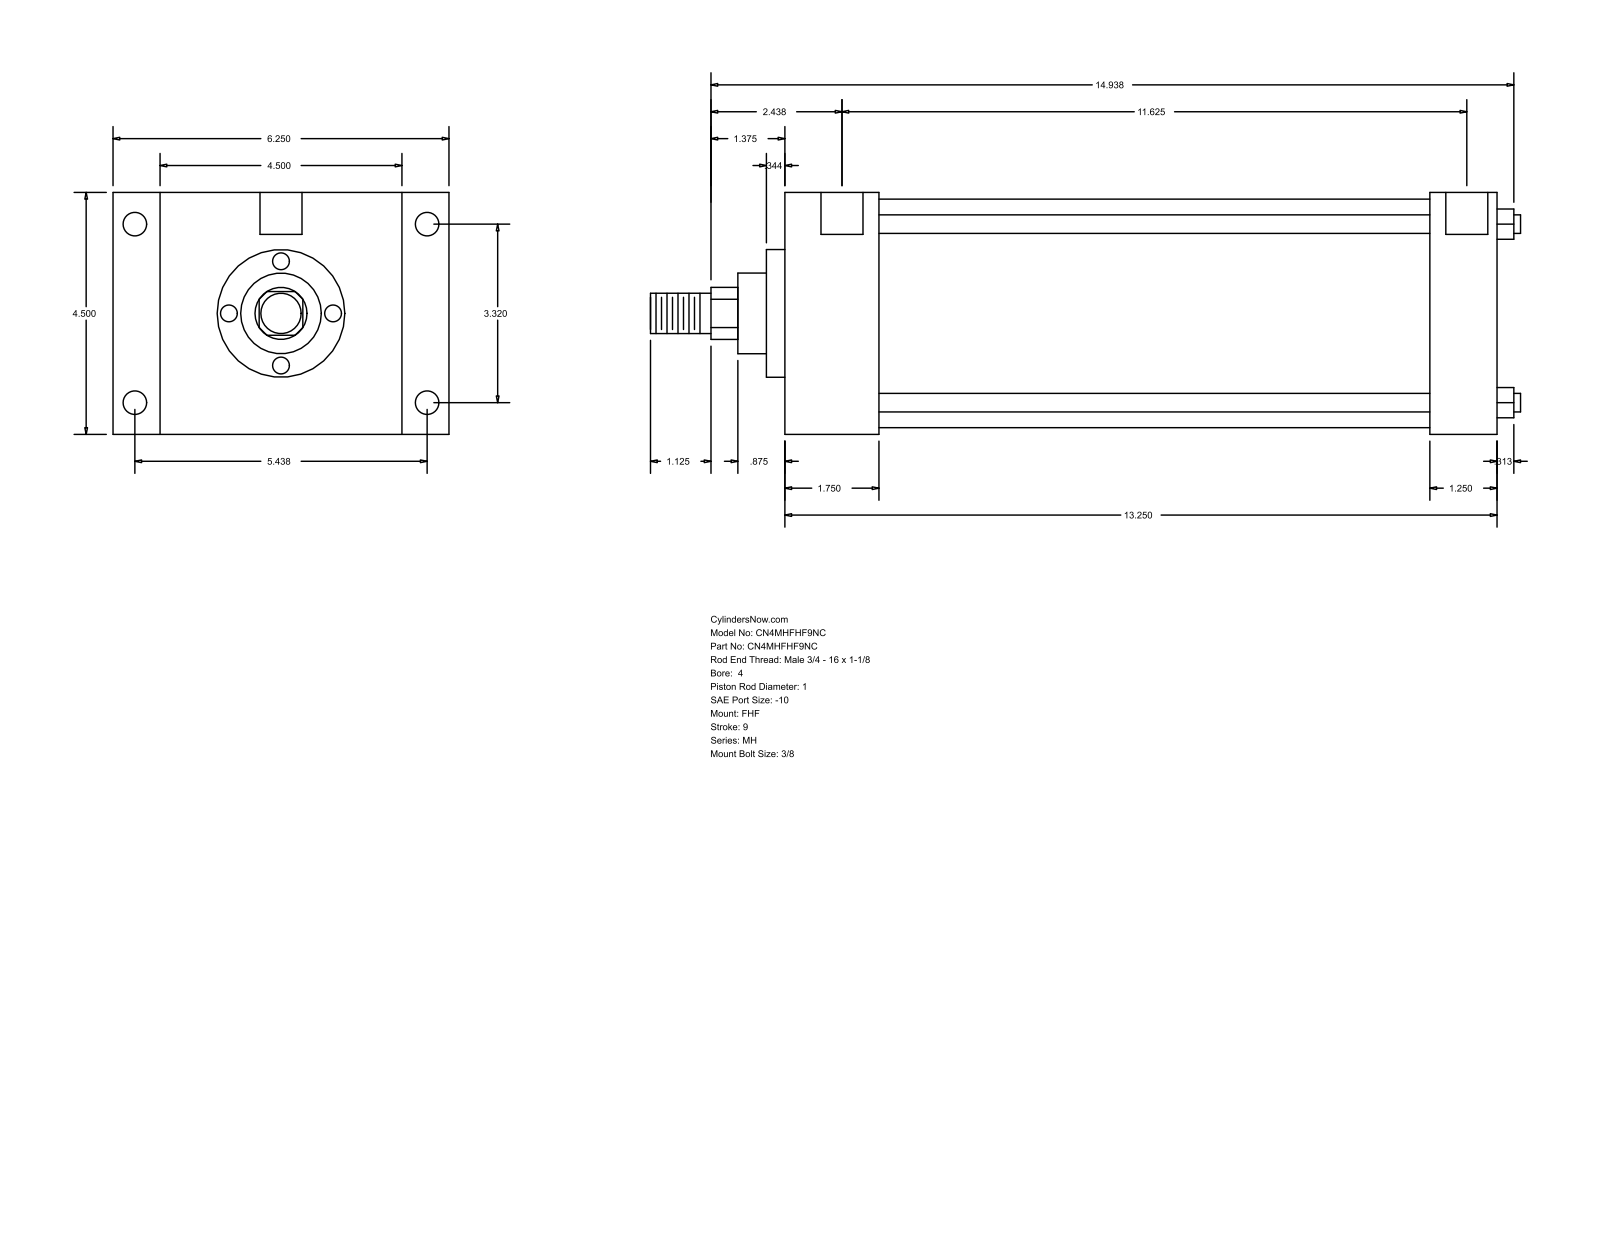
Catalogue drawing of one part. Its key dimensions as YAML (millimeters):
part_name: "MH_FHF__0400_1"
step_written_by: "GSSL Pune (CONFIG_CONTROL_DESIGN)"
units: millimeters
bodies: {solids: 0, faces: 90, planar: 61, cylindrical: 29, other: 0}
overall_size: [411.16, 158.75, 114.3]
round_holes:
  - {diameter: 8.73, count: 4}
  - {diameter: 11.13, count: 4}
  - {diameter: 19.84, count: 2}
round_bosses_or_shafts:
  - {diameter: 8.76, count: 4}
  - {diameter: 107.95, count: 1}
  - {diameter: 60.33, count: 1}
  - {diameter: 38.1, count: 1}
  - {diameter: 25.4, count: 1}
  - {diameter: 19.05, count: 1}
partial_cylinders:
  - {radius: 12.29, count: 1}
face_to_face_distances: [114.3, 336.56, 44.46, 292.1, 22.23, 136.53, 158.76, 304.81, 260.35, 31.75]
hole_center_spacings: [1.58, 84.32, 138.12, 161.82, 296.86, 298.44, 295.28]
